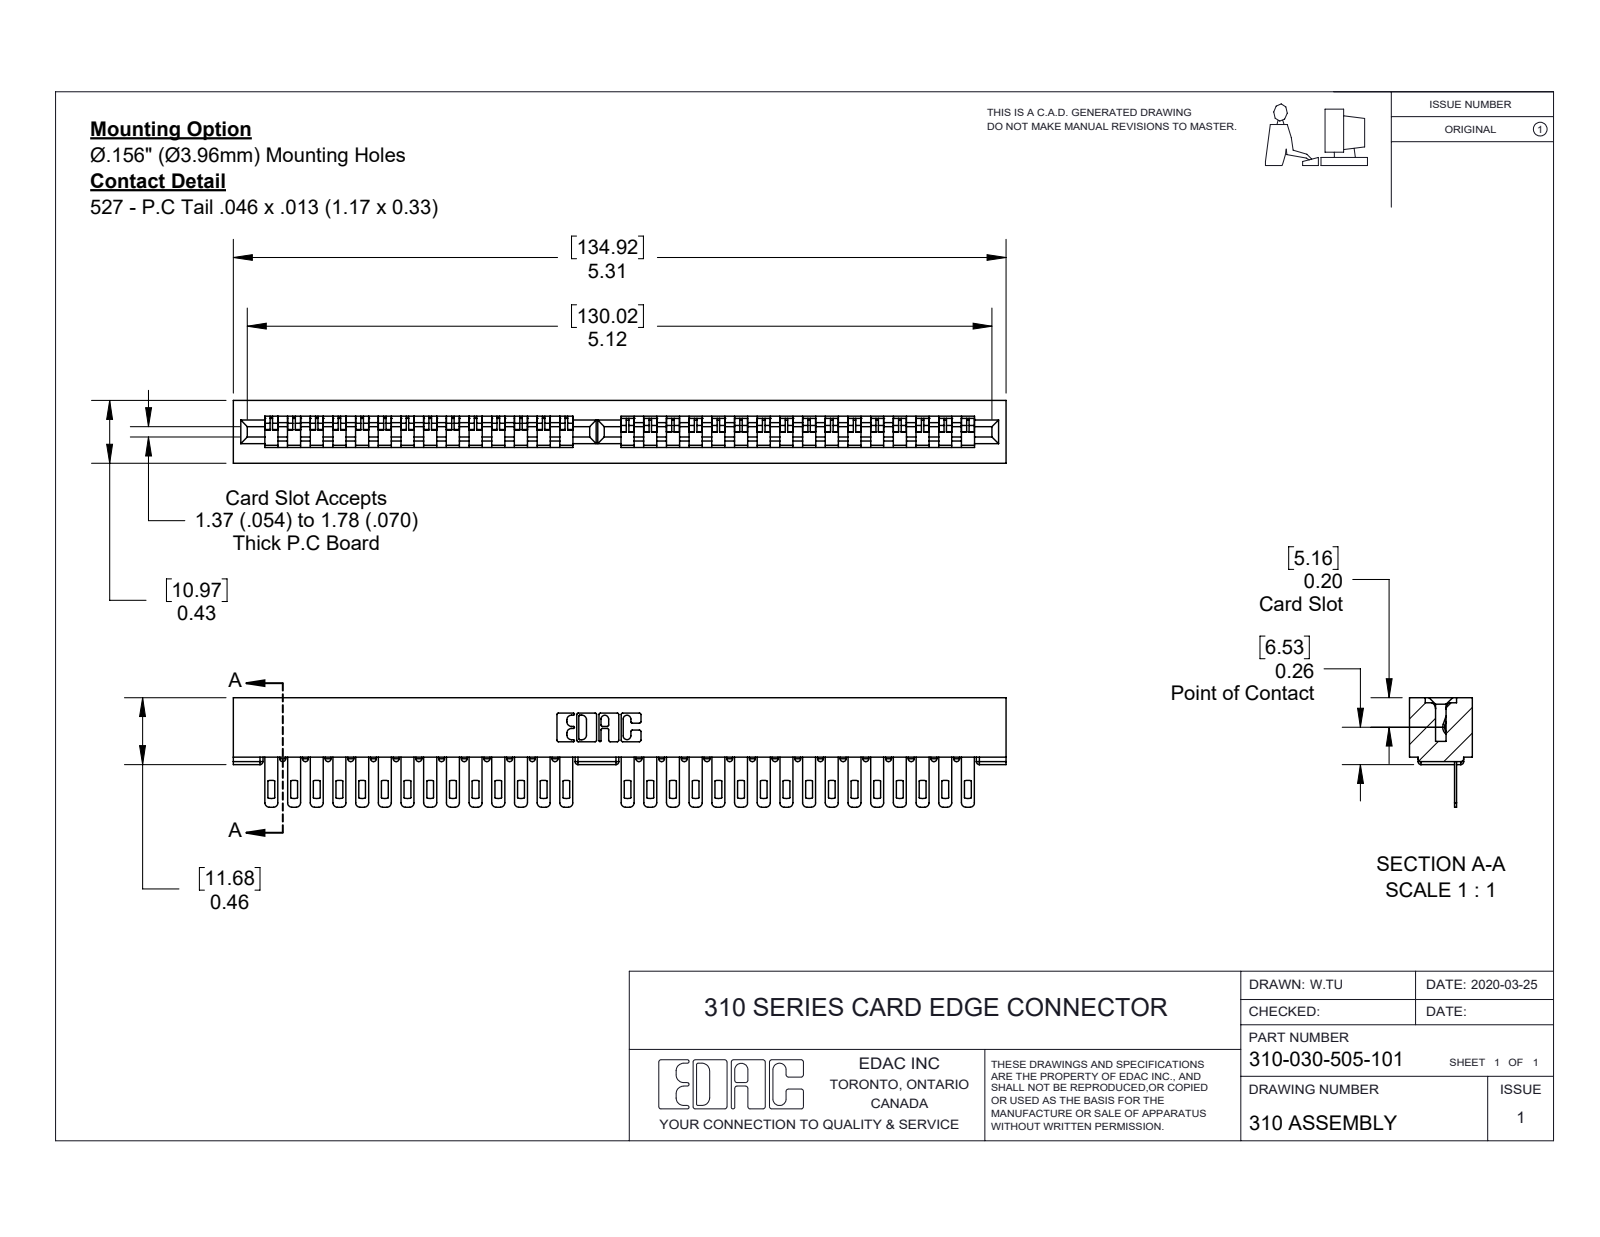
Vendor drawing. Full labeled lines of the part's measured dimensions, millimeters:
Part name (STEP PRODUCT): 307-290-001_505; 310-030-505-101; 310 Part_No Mounting Lugs
STEP written by: SolidWorks 2016 (CONFIG_CONTROL_DESIGN)
Units: millimetres
Bodies: 31 solids, 1838 faces (1160 planar, 614 cylindrical, 64 other)
Overall size (bounding box): 134.93 × 19.13 × 10.97
Volume: 11 709 mm³ · Surface area: 14 376 mm²
Partial cylindrical surfaces — rounded edges, fillets, slot ends (radius × count): R0.51 ×98, R0.76 ×60, R1.59 ×30, R0.25 ×22, R0.17 ×6, R0.8 ×6, R0.67 ×3, R0.3 ×2
Main face-to-face distances: 2.76, 8.22, 10.98, 0.38, 0.33, 1.82, 10.38, 5.46, 3.14, 7.84
